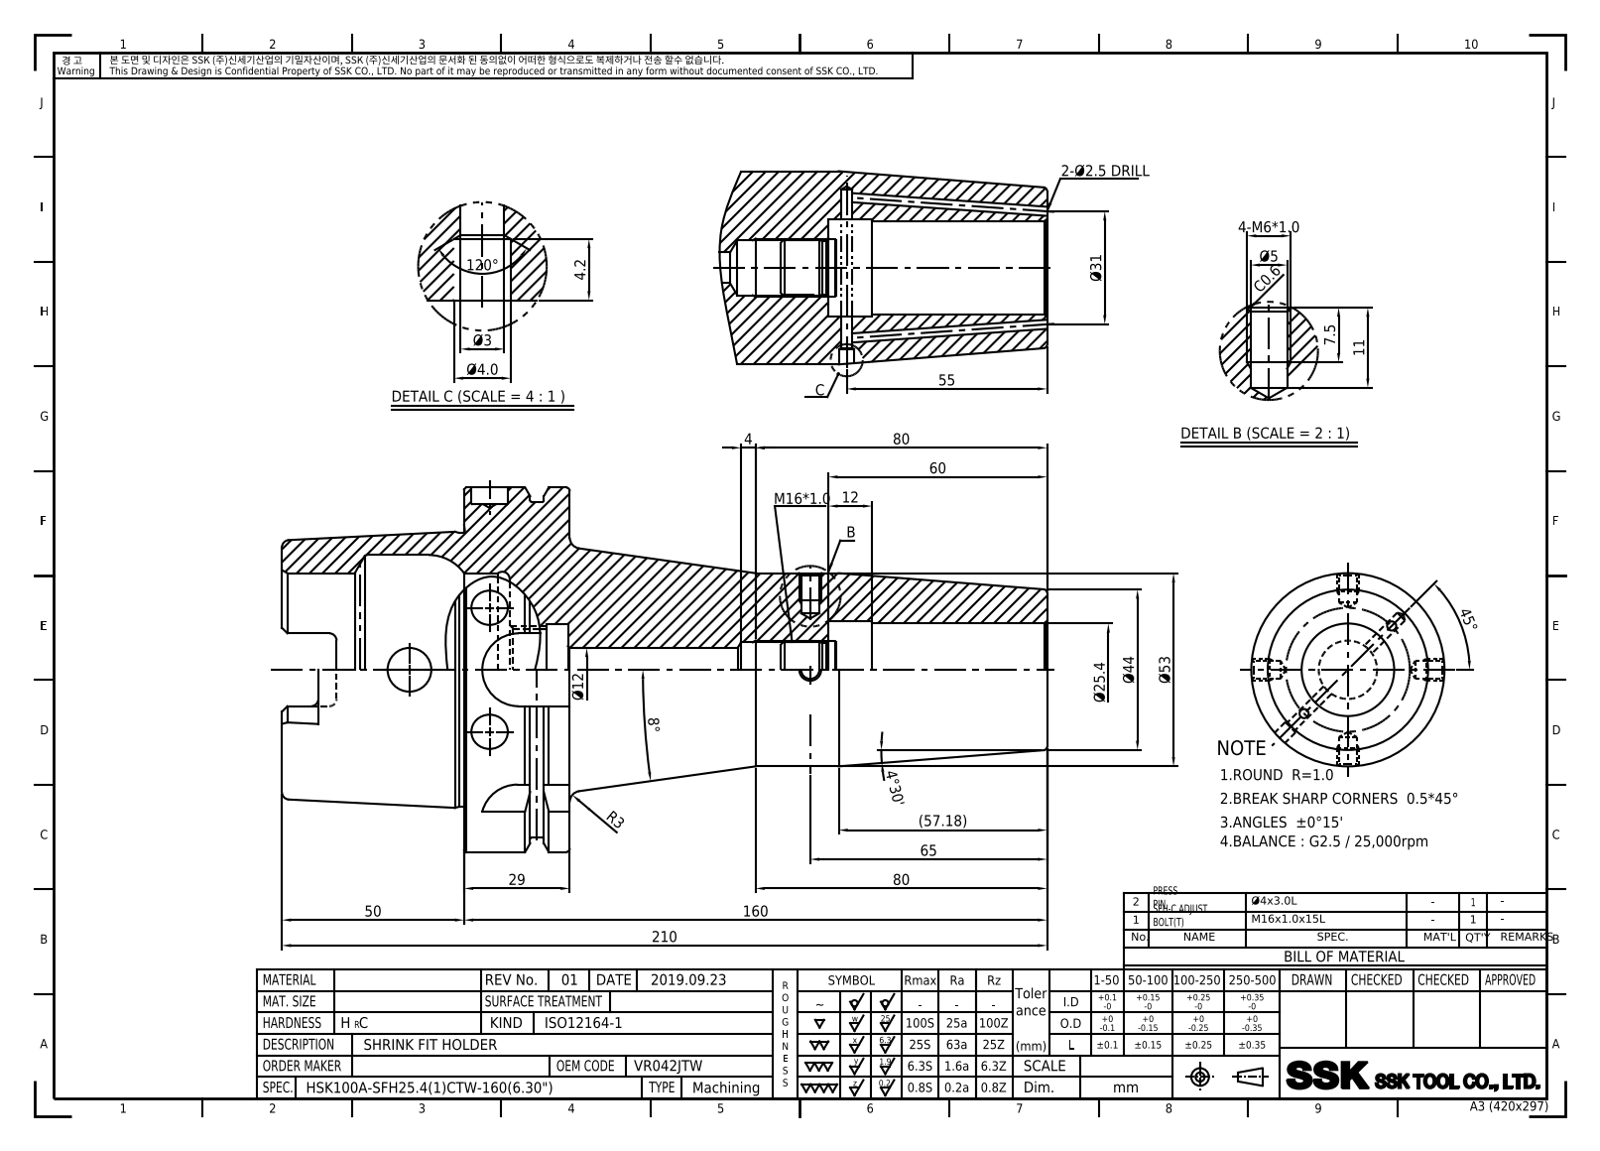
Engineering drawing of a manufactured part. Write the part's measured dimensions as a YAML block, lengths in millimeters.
part_name: "LO-HSK100A-SFH25.4CTW-160"
step_written_by: "Autodesk Inventor 2022 (AUTOMOTIVE_DESIGN)"
units: millimeters
bodies: {solids: 1, faces: 120, planar: 38, cylindrical: 37, other: 45}
overall_size: [210, 100, 100]
volume: 515368
surface_area: 78234
round_holes:
  - {diameter: 2, count: 2}
  - {diameter: 12, count: 2}
  - {diameter: 10, count: 1}
  - {diameter: 14.92, count: 1}
  - {diameter: 22.38, count: 1}
  - {diameter: 25, count: 1}
  - {diameter: 25.4, count: 1}
  - {diameter: 26.6, count: 1}
  - {diameter: 53, count: 1}
  - {diameter: 63, count: 1}
round_bosses_or_shafts:
  - {diameter: 100, count: 1}
  - {diameter: 92, count: 1}
  - {diameter: 75.41, count: 1}
partial_cylinders:
  - {radius: 2, count: 6}
  - {radius: 4.88, count: 4}
  - {radius: 10, count: 4}
face_to_face_distances: [29, 12.5, 16.5, 62.5, 50, 79, 210, 160, 147.5, 131]
